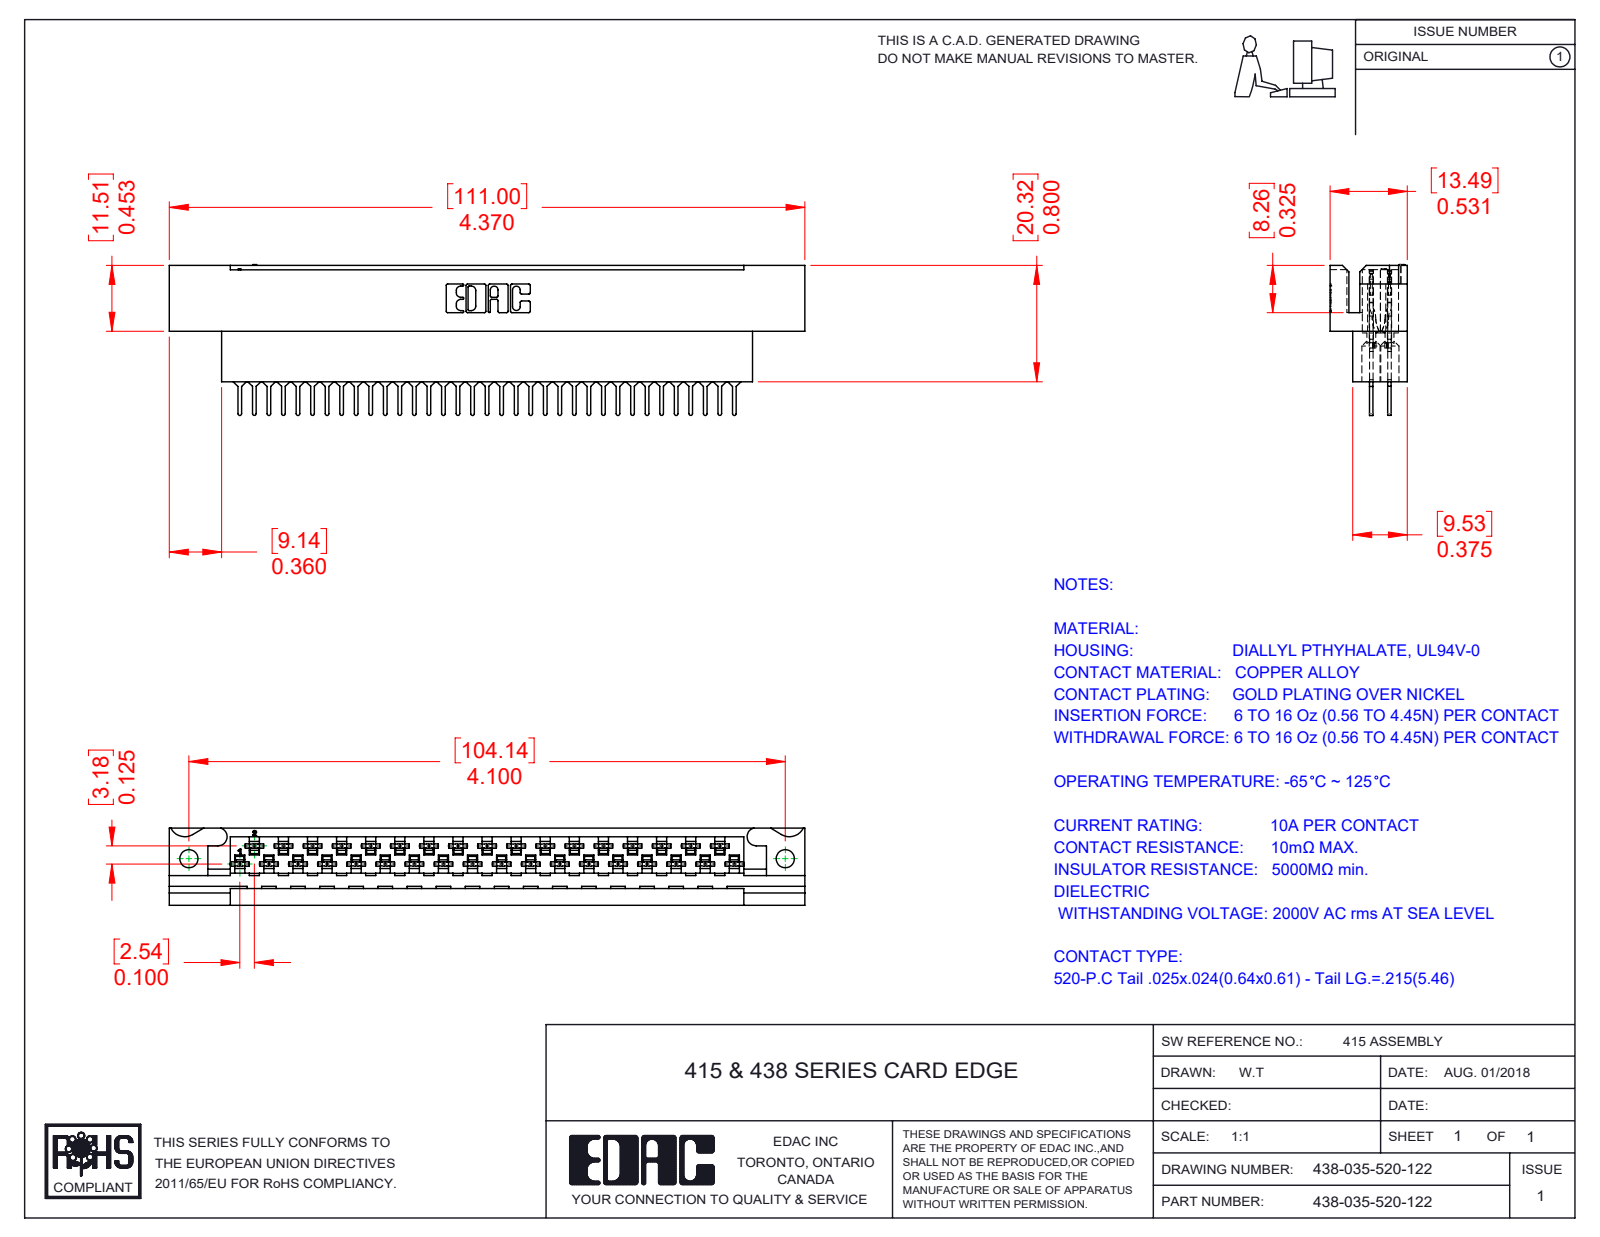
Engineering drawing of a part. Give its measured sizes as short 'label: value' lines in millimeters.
name: 438-210-001_438-210-035-112; 516-290-001_520; 438-035-520-122
written by: SolidWorks 2016 (CONFIG_CONTROL_DESIGN)
unit: mm
bodies: 36 solids, 3586 faces (2289 planar, 960 cylindrical, 337 other)
size: 111 × 26.32 × 13.49
volume: 18 143 mm³; area: 22 558 mm²
holes: 35× ⌀1.27, 35× ⌀3.3, 1× ⌀3.17, 1× ⌀3.18
rounds: 140× R0.3, 140× R0.56, 70× R0.18, 70× R0.2, 70× R0.41, 70× R2.03, 35× R0.32, 22× R0.25
face distances: 3.18, 1.88, 0.61, 1.27, 13.49, 2.92, 3.96, 7.49, 3.58, 6.61
hole spacings: 5.08, 10.16, 15.24, 20.32, 25.4, 30.48, 35.56, 2.54
